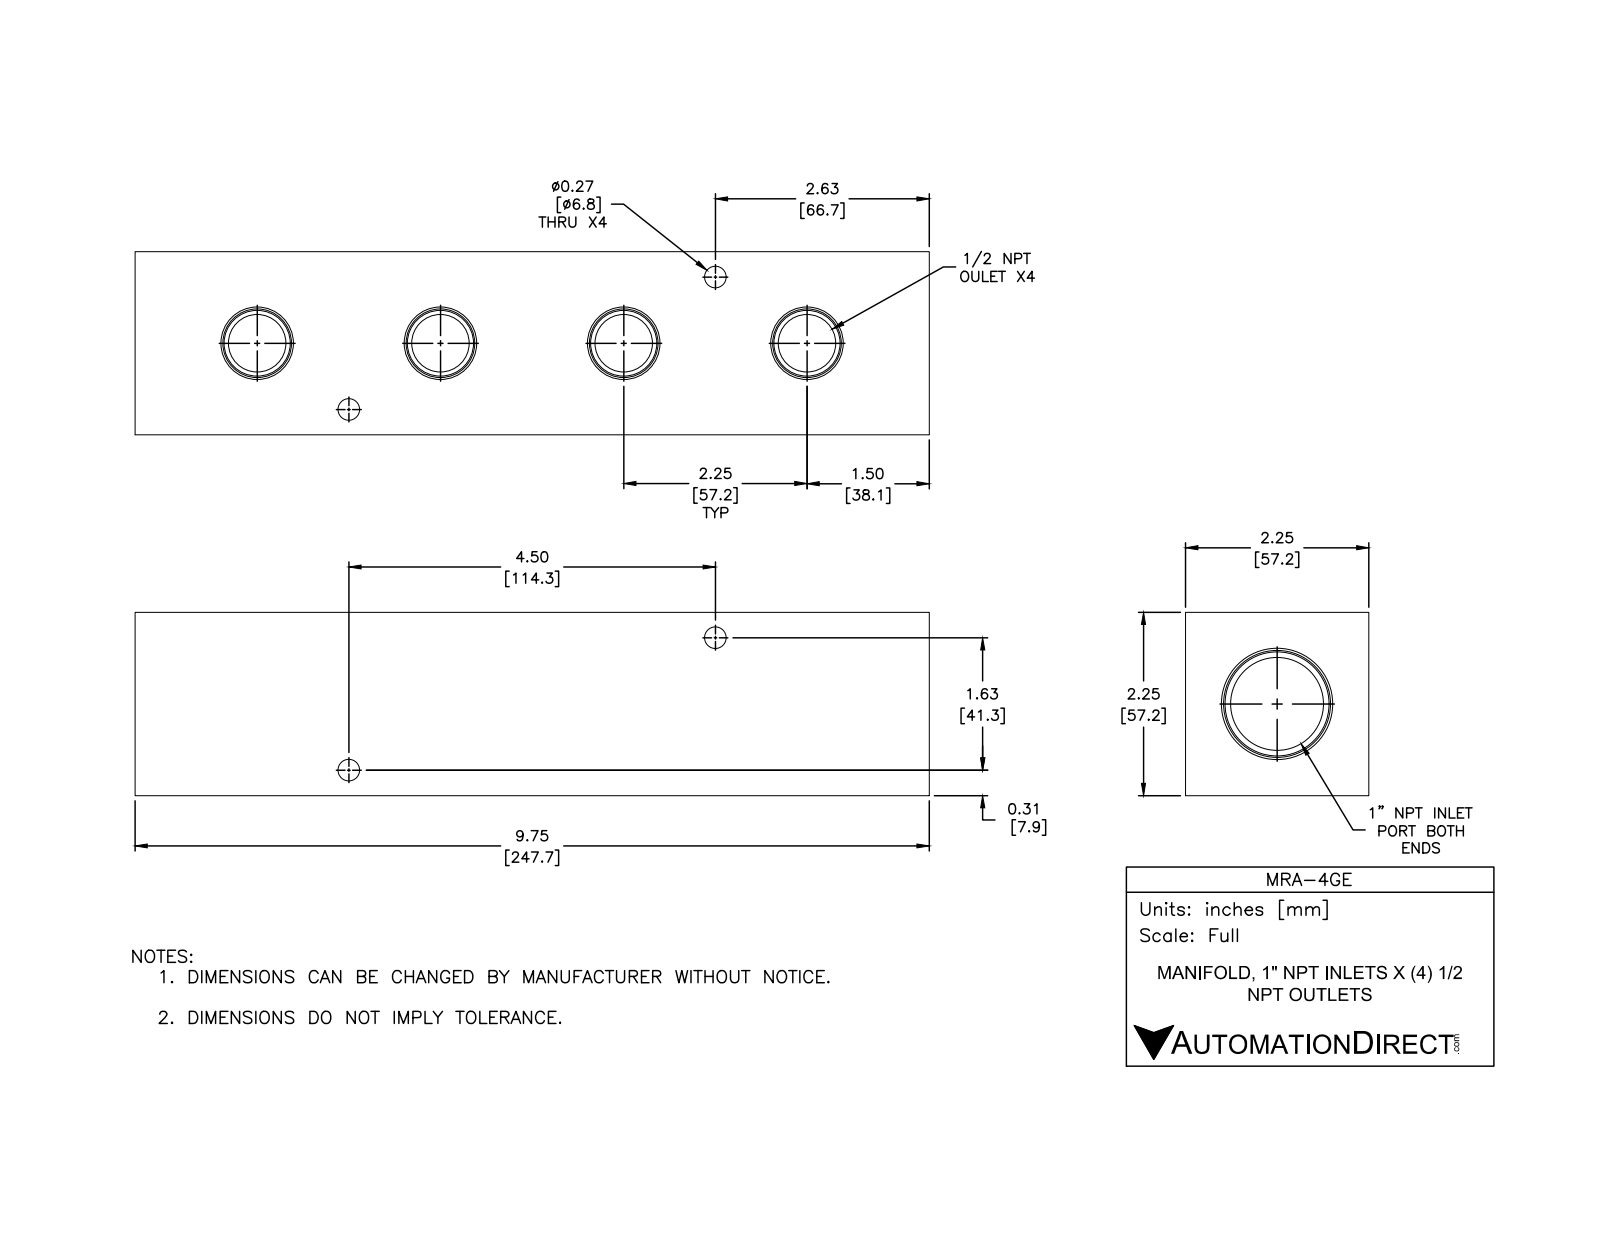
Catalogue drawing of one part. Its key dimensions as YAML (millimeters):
part_name: "MRA-4GE"
step_written_by: "SolidWorks 2015 (CONFIG_CONTROL_DESIGN)"
units: millimeters
bodies: {solids: 1, faces: 62, planar: 12, cylindrical: 26, other: 24}
overall_size: [247.7, 57.2, 57.2]
volume: 611200
surface_area: 90580
round_holes:
  - {diameter: 6.8, count: 4}
  - {diameter: 17.9, count: 4}
  - {diameter: 29, count: 1}
face_to_face_distances: [57.2, 247.7, 16.8, 230.9, 43.7, 13.5, 214.1]
hole_center_spacings: [35.3, 57.2, 121.5, 144.3, 57.2, 88.2, 88.2, 114.3]
